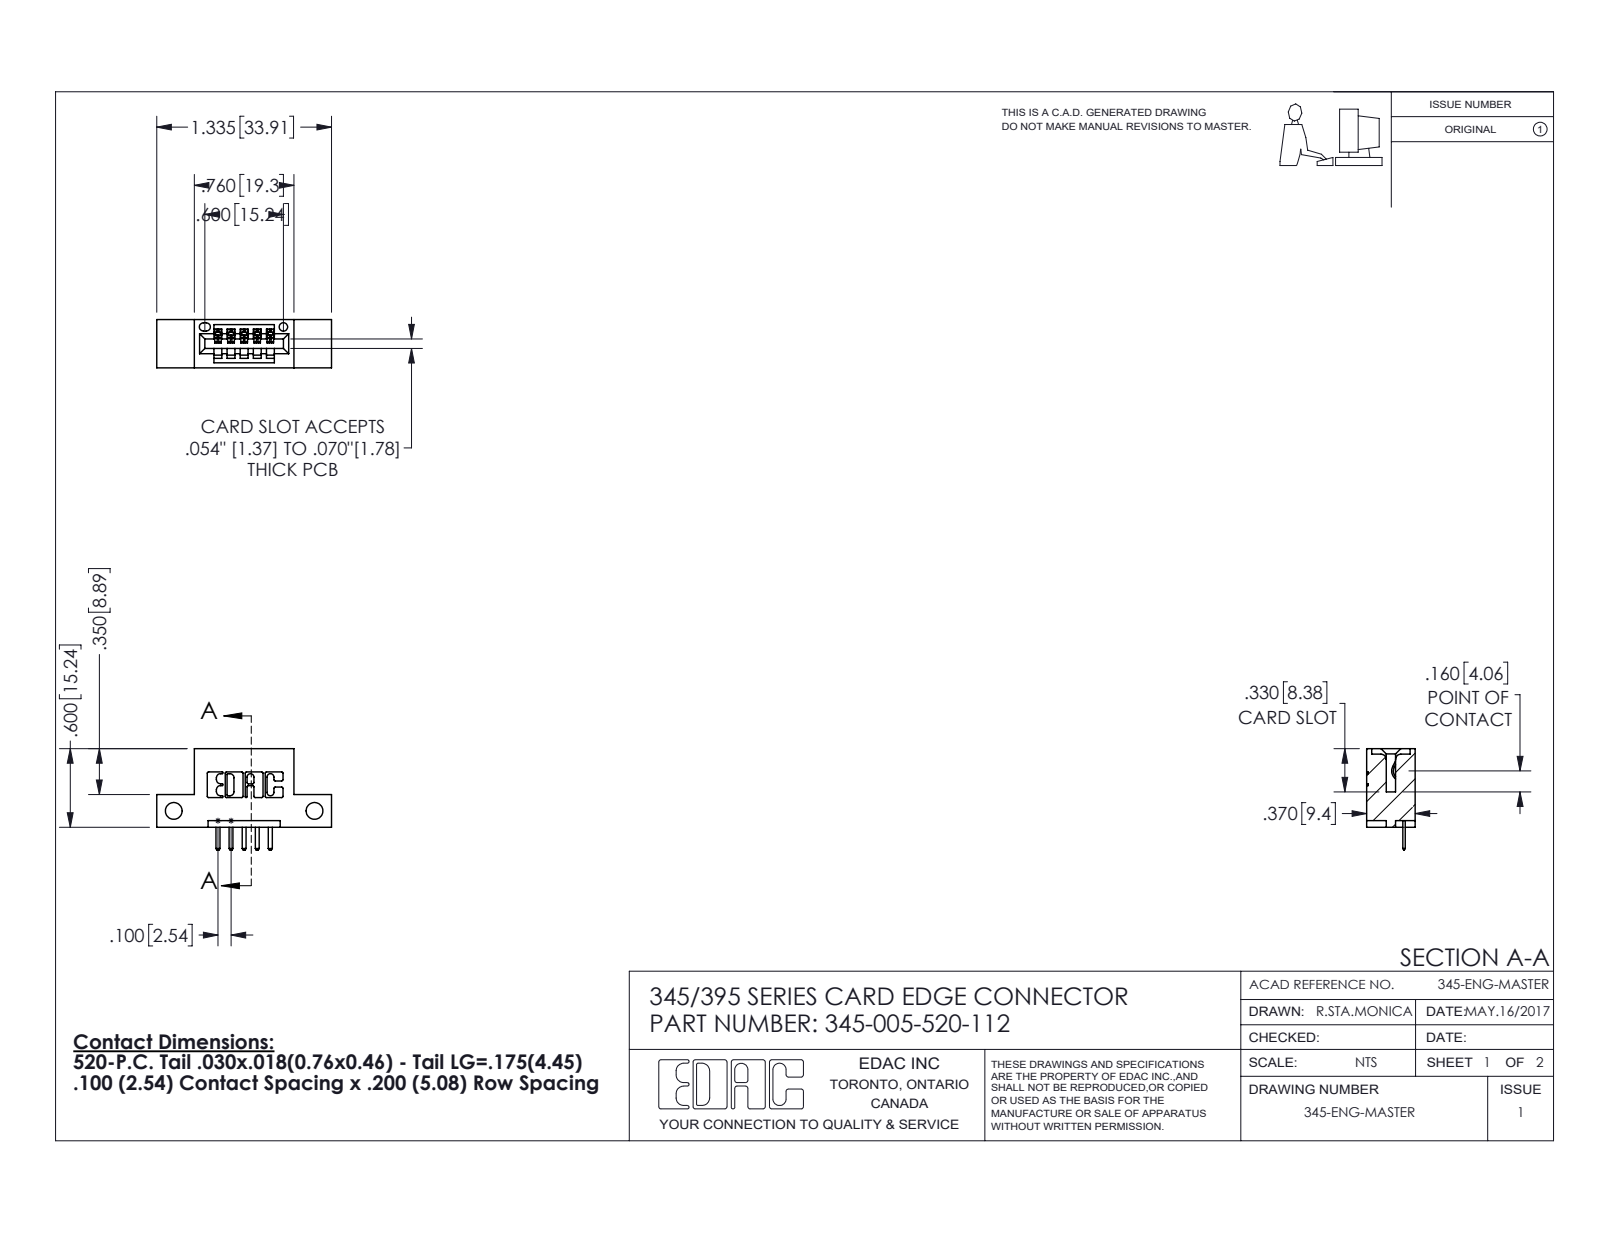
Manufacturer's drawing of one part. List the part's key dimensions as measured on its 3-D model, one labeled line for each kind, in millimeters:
Part name (STEP PRODUCT): 345 Part_Flush Mounting Lugs - Side Mount; 345-005-520-112; 345-292-001_345-293-120
STEP written by: SolidWorks 2016 (CONFIG_CONTROL_DESIGN)
Units: millimetres
Bodies: 6 solids, 436 faces (290 planar, 146 cylindrical, 0 other)
Overall size (bounding box): 33.9 × 19.7 × 9.4
Volume: 2 820 mm³ · Surface area: 3 050 mm²
Round holes (diameter × count): ⌀3.3 ×2, ⌀1.6 ×1
Partial cylindrical surfaces — rounded edges, fillets, slot ends (radius × count): R0.3 ×22, R0.3 ×12, R0.2 ×10, R0.2 ×6, R0.8 ×6, R0.7 ×3, R0.8 ×2, R1 ×2
Main face-to-face distances: 5.1, 9.4, 2.5, 7.6, 1.8, 6.4, 1.5, 0.6, 14, 8.9
Hole centre spacings: 27.3
